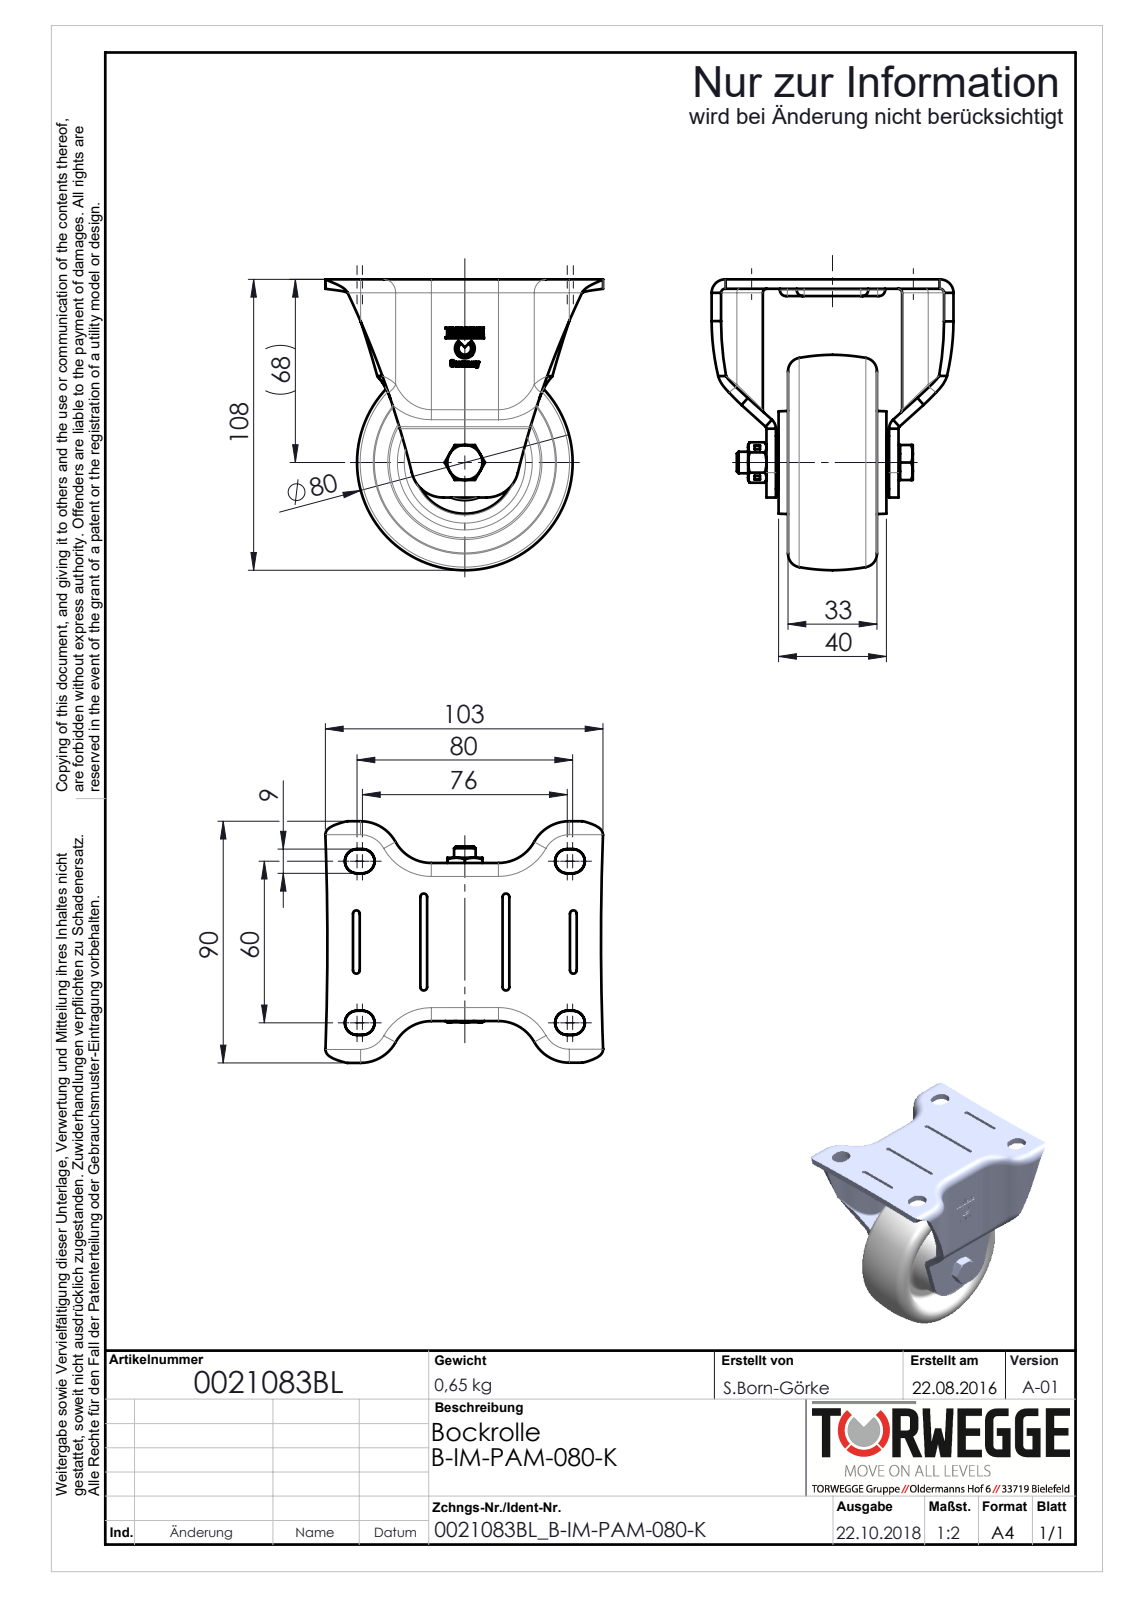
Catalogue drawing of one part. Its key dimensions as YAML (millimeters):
part_name: "0021083BL_B-IM-PAM-080-K"
step_written_by: "SolidWorks 2016 (AUTOMOTIVE_DESIGN)"
units: millimeters
bodies: {solids: 0, faces: 687, planar: 323, cylindrical: 194, other: 170}
overall_size: [108, 103.04, 89.74]
round_holes:
  - {diameter: 6.8, count: 1}
  - {diameter: 8, count: 1}
  - {diameter: 8.2, count: 1}
  - {diameter: 12, count: 1}
  - {diameter: 12.4, count: 1}
  - {diameter: 23.2, count: 1}
round_bosses_or_shafts:
  - {diameter: 20, count: 1}
  - {diameter: 16.8, count: 1}
  - {diameter: 13, count: 1}
  - {diameter: 11.9, count: 1}
partial_cylinders:
  - {radius: 4.5, count: 10}
  - {radius: 5, count: 9}
  - {radius: 0.27, count: 8}
  - {radius: 1.25, count: 8}
  - {radius: 2.2, count: 8}
  - {radius: 2.75, count: 8}
  - {radius: 0.15, count: 7}
  - {radius: 0.45, count: 7}
face_to_face_distances: [3.5, 45.5, 4.85, 50.35, 4.5, 1, 44.5, 41, 42, 49]
